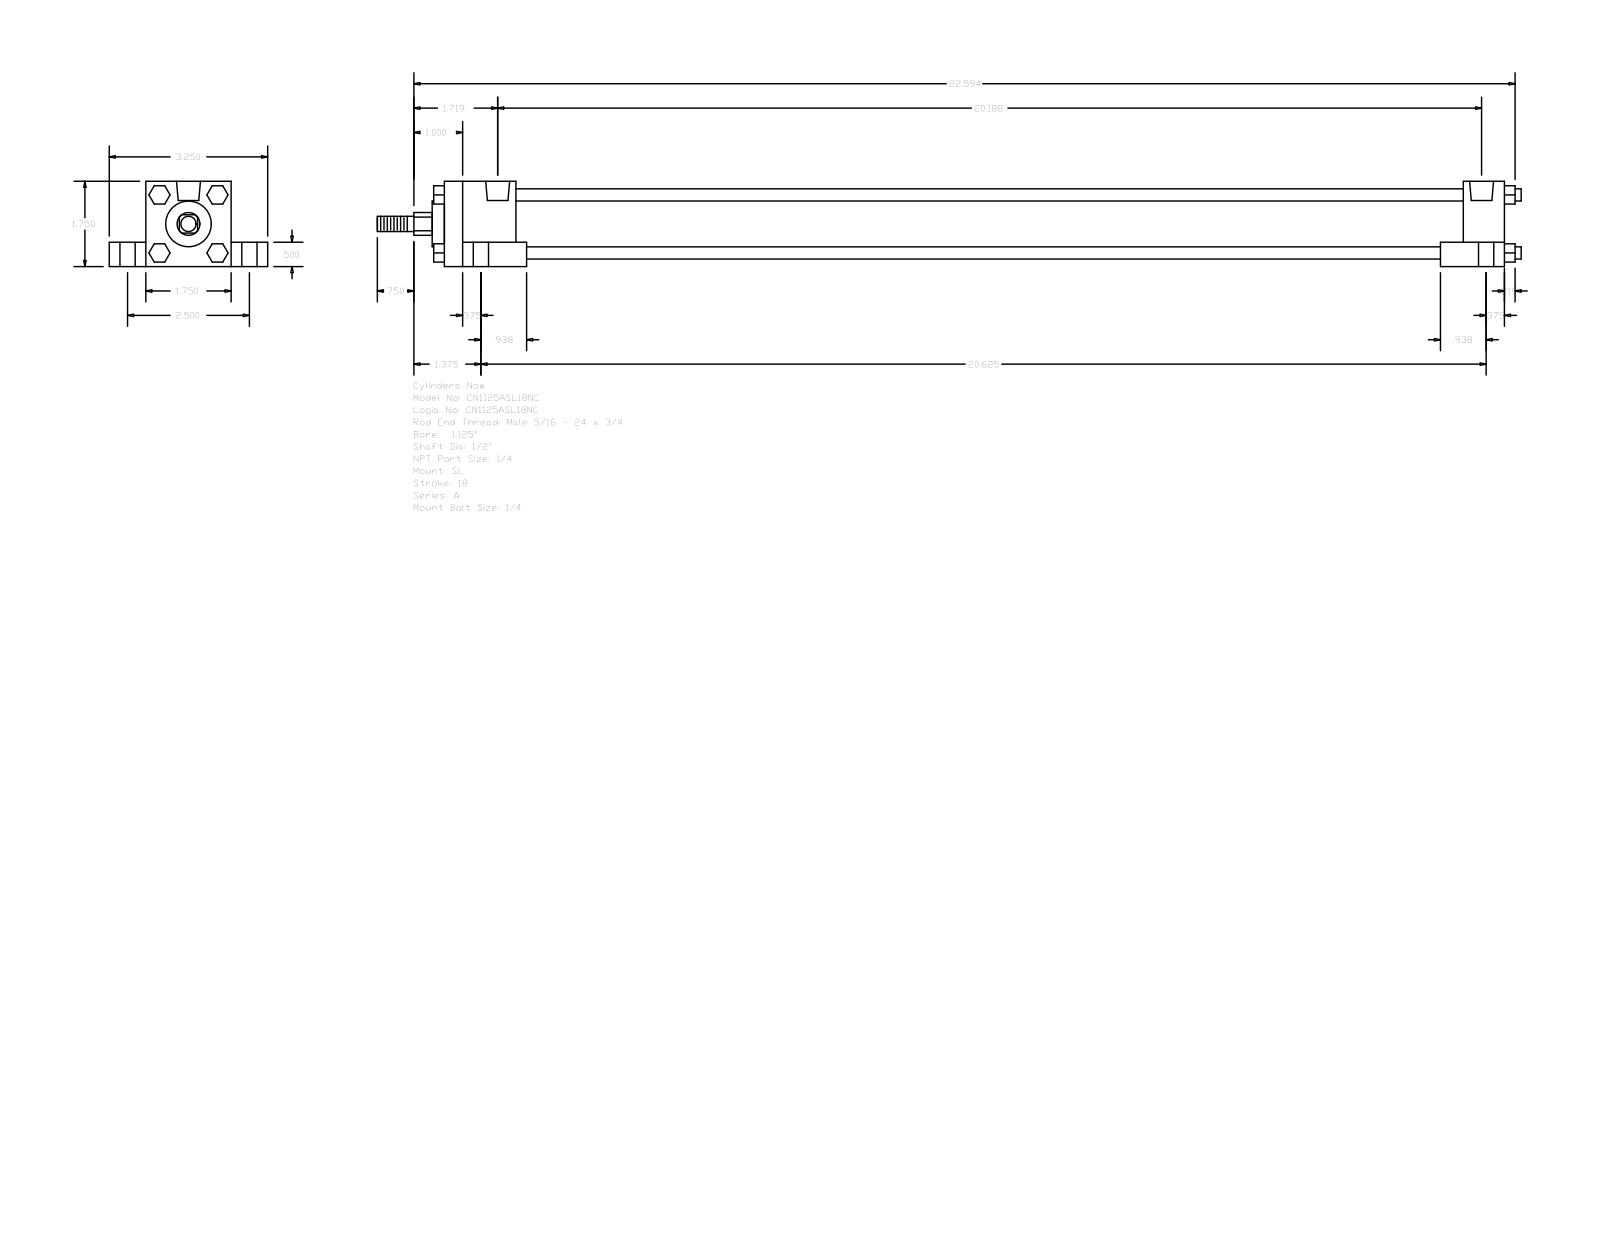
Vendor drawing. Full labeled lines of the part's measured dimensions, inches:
Part name (STEP PRODUCT): A_SL__0112_0.5
STEP written by: GSSL Pune (CONFIG_CONTROL_DESIGN)
Units: inches
Bodies: 0 solids, 150 faces (114 planar, 36 cylindrical, 0 other)
Overall size (bounding box): 23.469 × 3.25 × 1.75
Round holes (diameter × count): ⌀0.219 ×4, ⌀0.313 ×4, ⌀0.563 ×4, ⌀0.492 ×2
Round bosses / shafts (diameter × count): ⌀0.25 ×4, ⌀1.255 ×1, ⌀0.937 ×1, ⌀0.5 ×1, ⌀0.313 ×1
Partial cylindrical surfaces — rounded edges, fillets, slot ends (radius × count): R0.234 ×1
Main face-to-face distances: 1.75, 1.25, 0.5, 0.75, 2.5, 21.75, 20.906, 0.844, 1.469, 19.437
Hole centre spacings: 1.254, 1.26, 1.296, 1.315, 2.5, 20.063, 20.257, 20.32
